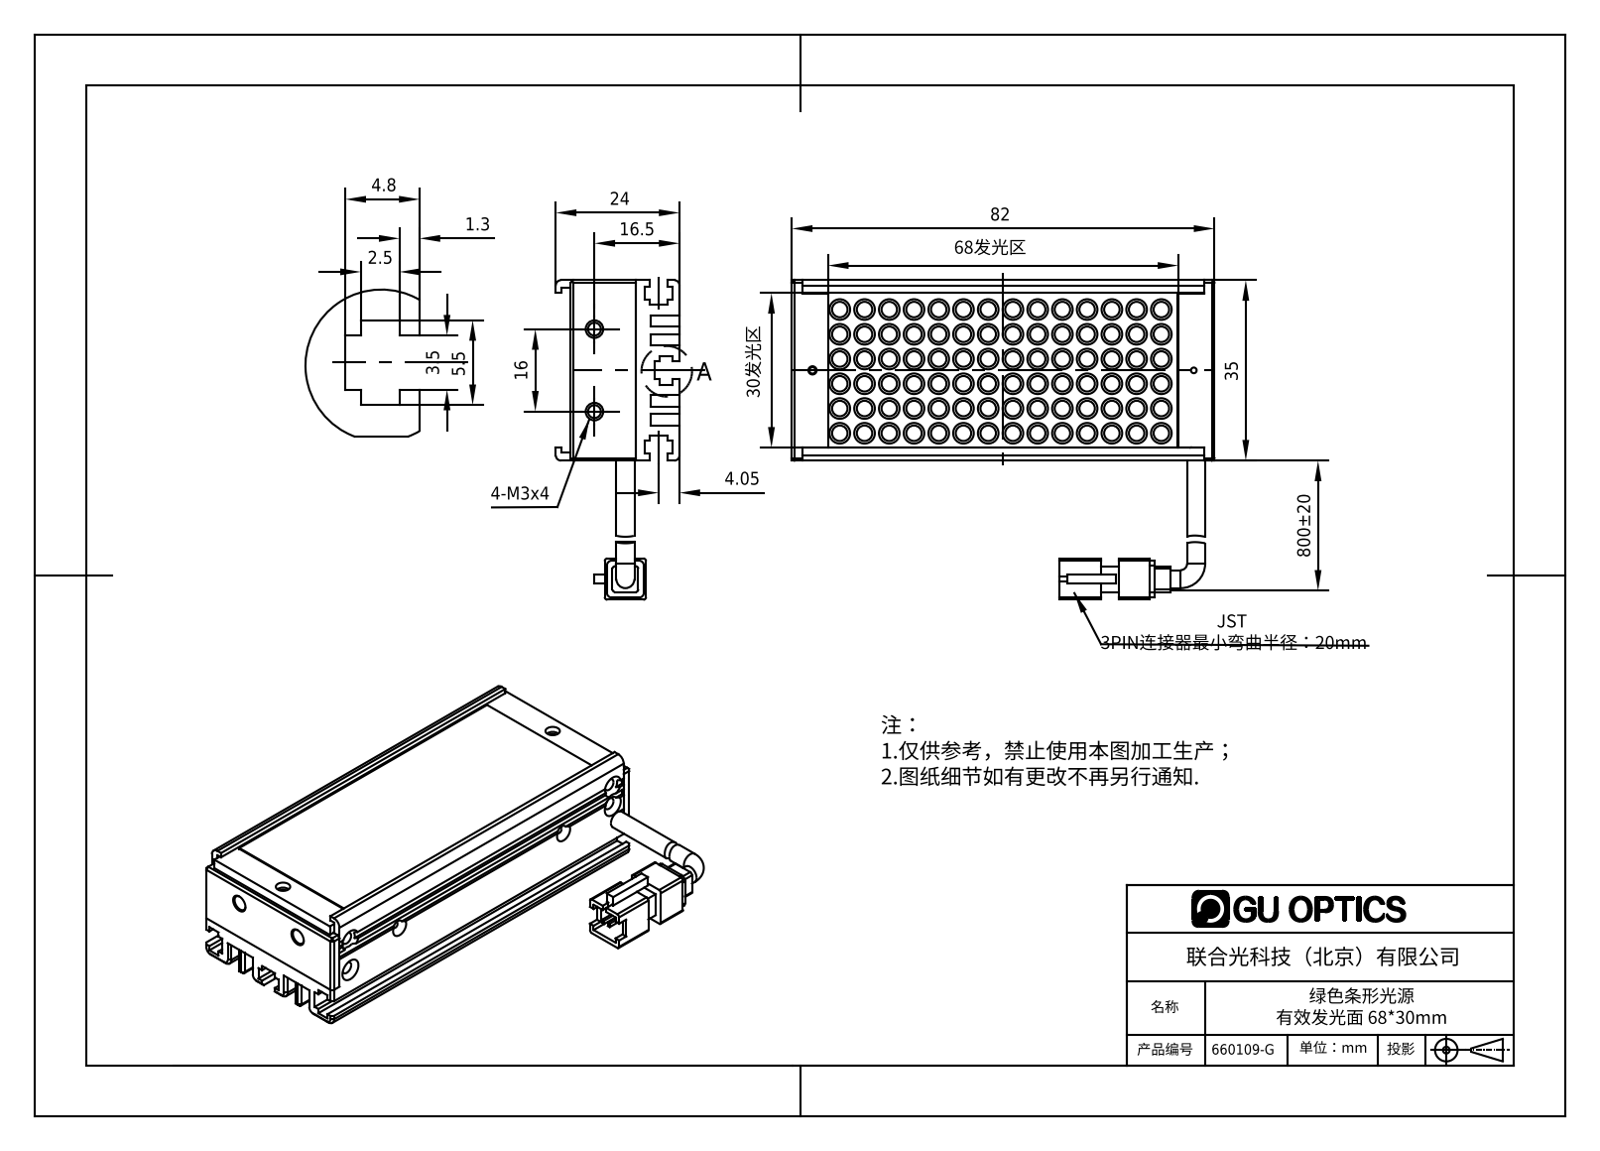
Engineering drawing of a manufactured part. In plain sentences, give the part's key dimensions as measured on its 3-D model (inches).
The part is named "660109-G". Its 3-D file was written by "SolidWorks 2016 (AUTOMOTIVE_DESIGN)". It is 8 solids with 823 faces: 326 planar, 272 cylindrical and 225 other. Overall it measures 3.228 by 2.441 by 0.945 inches. Its volume is 2.289 cubic inches and its surface area 65.07 square inches. Round holes: 5 of diameter 0.063, 5 of diameter 0.094, 4 of diameter 0.049, 2 of diameter 0.059, 2 of diameter 0.098, 2 of diameter 0.11, 2 of diameter 0.118. Round bosses or shafts: 84 of diameter 0.122, 2 of diameter 0.138. Partial cylindrical surfaces (rounded edges, fillets, slot ends): 12 of radius 0.02, 8 of radius 0.039, 8 of radius 0.059, 2 of radius 0.065. The main face-to-face distances are 0.079, 0.087, 0.402, 0.315, 0.551, 0.472, 0.098, 0.394, 0.157, 0.339. The hole center spacings are 0.276, 2.835, 0.098, 0.177, 0.531, 0.543, 0.547, 0.551.
